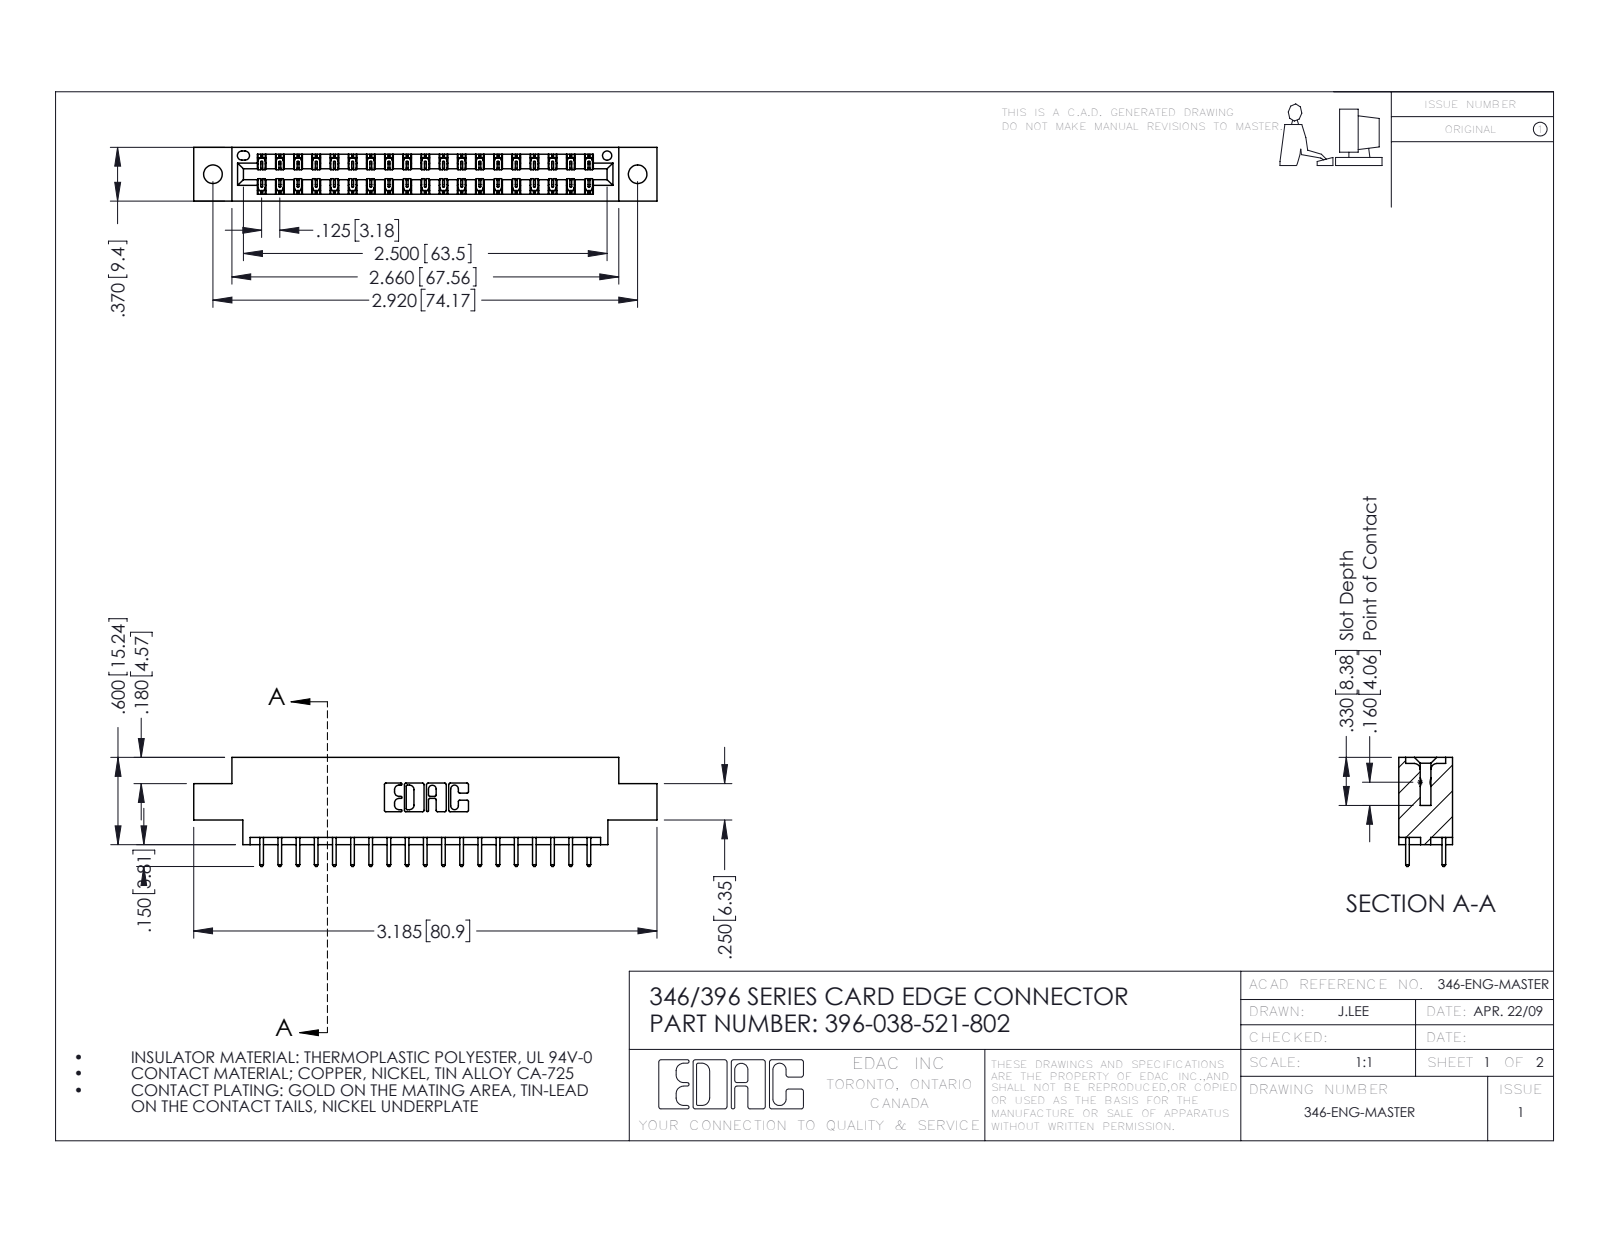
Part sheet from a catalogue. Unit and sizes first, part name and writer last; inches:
Units: inches
Overall size (bounding box): 3.185 × 0.75 × 0.37
Round holes (diameter × count): ⌀0.128 ×2, ⌀0.064 ×1
Partial cylindrical surfaces — rounded edges, fillets, slot ends (radius × count): R0.006 ×57, R0.01 ×38, R0.01 ×22, R0.007 ×6, R0.031 ×6, R0.026 ×3, R0.014 ×2, R0.022 ×2
Main face-to-face distances: 0.048, 0.322, 0.25, 0.37, 0.072, 0.298, 0.025, 0.275, 0.148, 0.222
Hole centre spacings: 0.246, 2.713, 2.92
Volume: 0.458 in³ · Surface area: 15.13 in²
Bodies: 39 solids, 2102 faces (1410 planar, 692 cylindrical, 0 other)
Part name (STEP PRODUCT): 345-292-001_345-293-121; 346 Part_0.170 Offset - 0.128 Dia; 396-038-521-802
STEP written by: SolidWorks 2016 (CONFIG_CONTROL_DESIGN)
